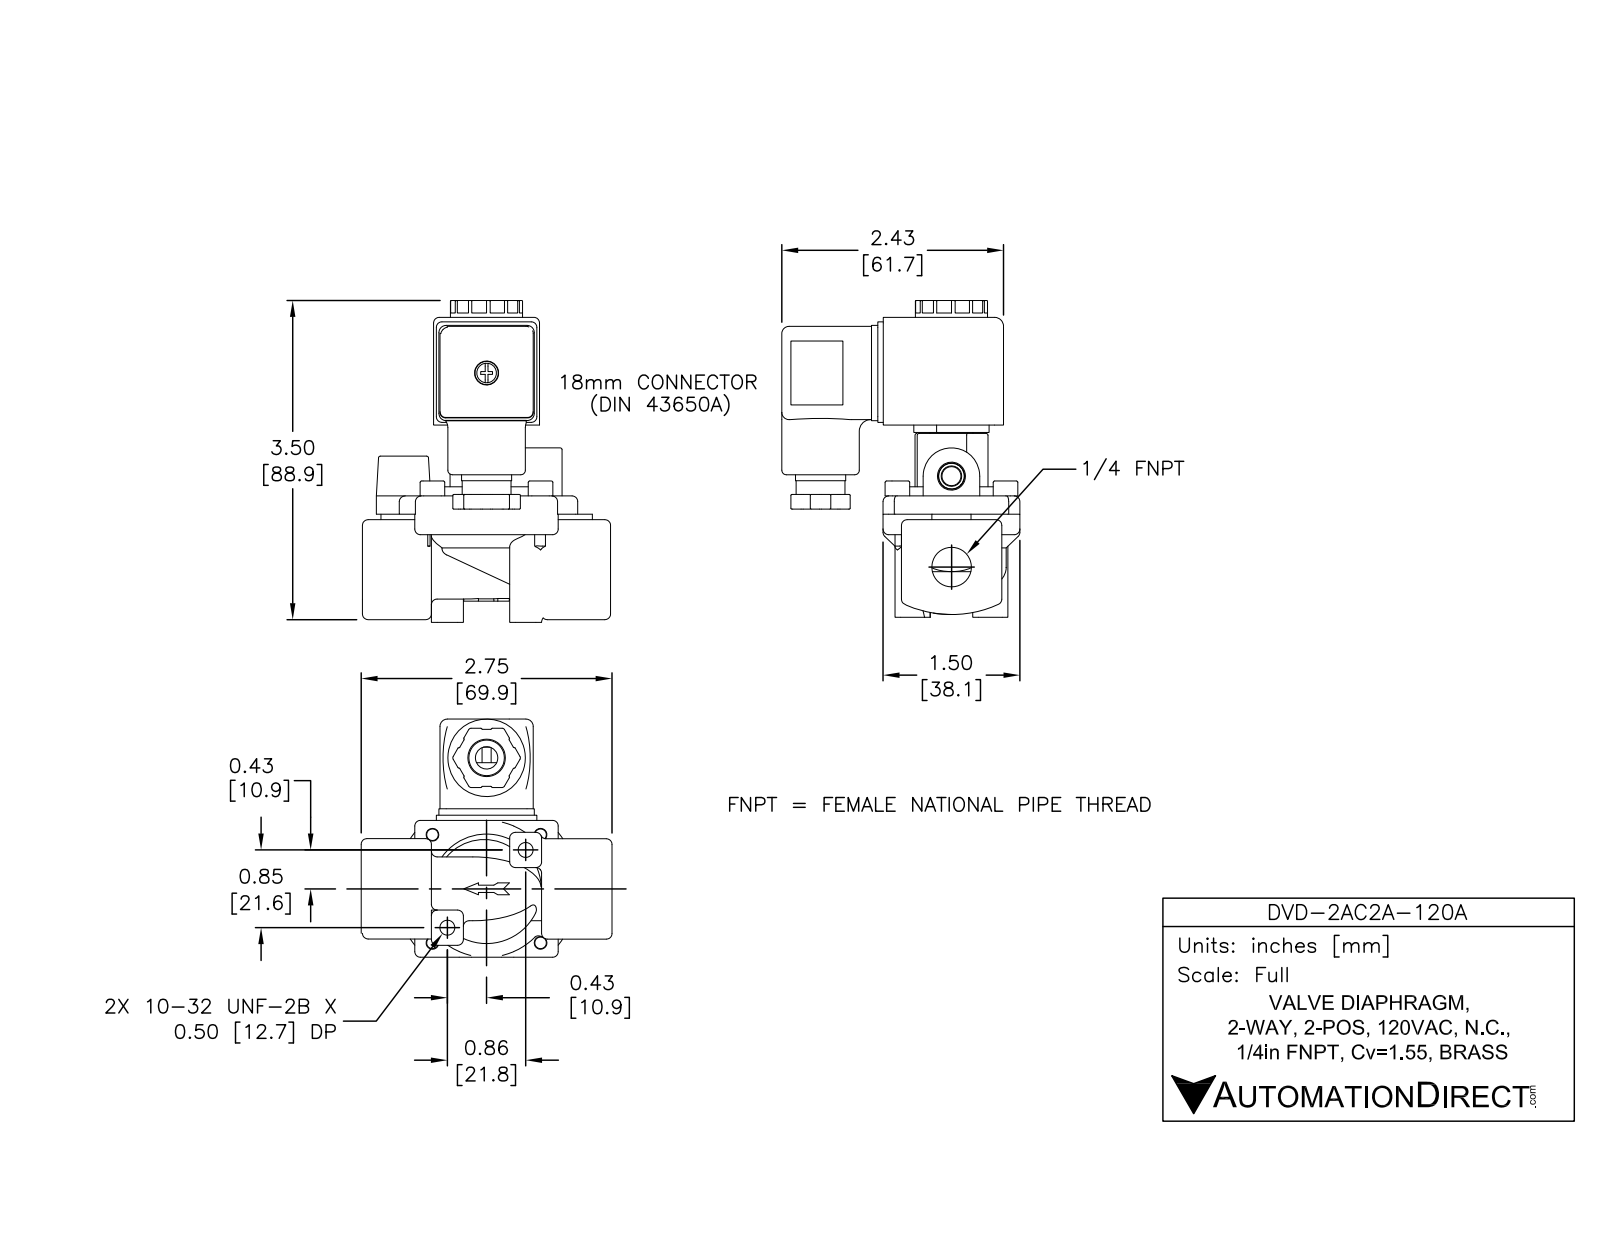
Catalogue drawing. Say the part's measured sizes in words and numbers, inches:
The part is named "DVD-2AC2A-120A". Its 3-D file was written by "SolidWorks 2015 (AUTOMOTIVE_DESIGN)". It is 1 solid with 1779 faces: 848 planar, 363 cylindrical and 568 other. Overall it measures 3.472 by 2.72 by 2.61 inches. Its volume is 5.884 cubic inches and its surface area 63.91 square inches. Round holes: 4 of diameter 0.139, 2 of diameter 0.06, 2 of diameter 0.098, 2 of diameter 0.14, 2 of diameter 0.164, 2 of diameter 0.434, 1 of diameter 0.062, 1 of diameter 0.077, 1 of diameter 0.089, 1 of diameter 0.093, 1 of diameter 0.102, 1 of diameter 0.12. Round bosses or shafts: 4 of diameter 0.27, 4 of diameter 0.16, 1 of diameter 1.375, 1 of diameter 0.85, 1 of diameter 0.79, 1 of diameter 0.609, 1 of diameter 0.535, 1 of diameter 0.405. Partial cylindrical surfaces (rounded edges, fillets, slot ends): 52 of radius 0.01, 29 of radius 0.063, 21 of radius 0.062, 12 of radius 0.08, 12 of radius 0.156, 8 of radius 0.05, 7 of radius 0.062, 6 of radius 0.03. The main face-to-face distances are 0.925, 1.161, 0.2, 0.08, 1.036, 1.1, 1.181, 0.956, 1.3, 0.06. The hole center spacings are 0.924, 0.838, 1.185, 0.233, 0.389, 0.449, 0.605, 0.672.
